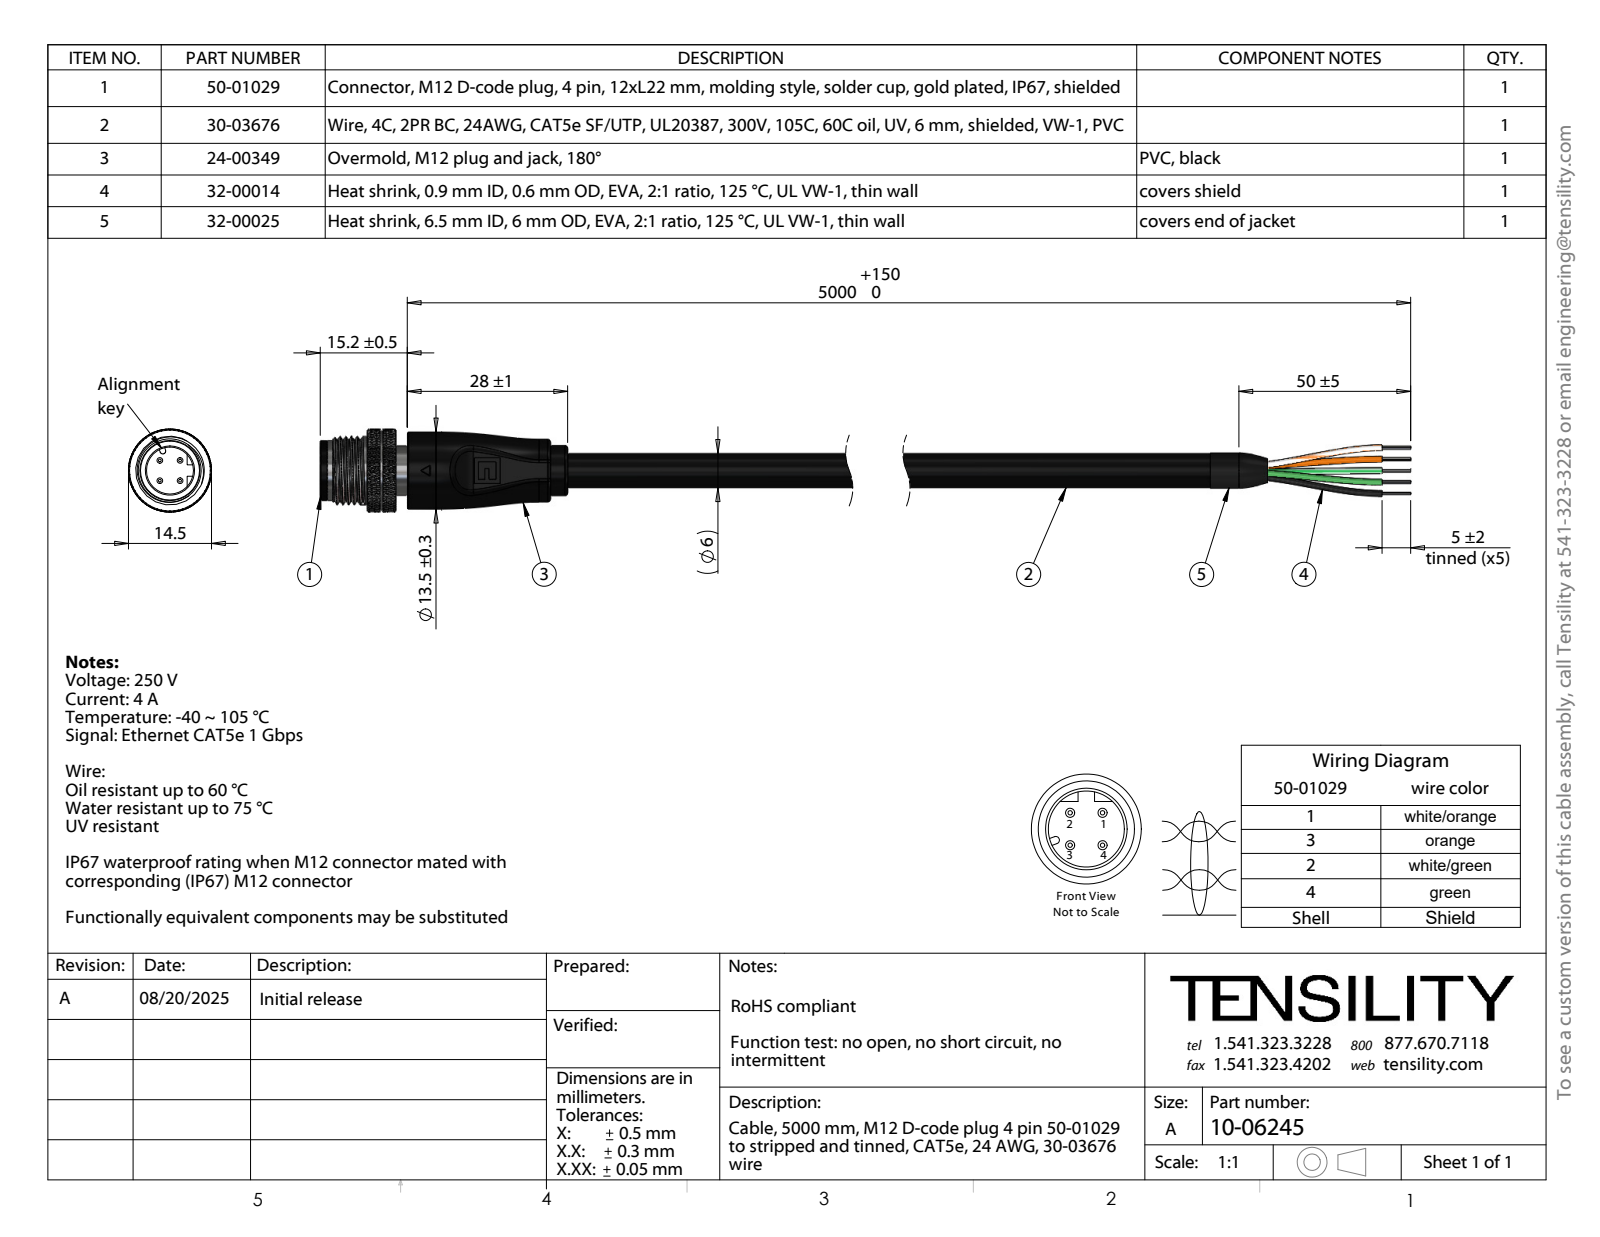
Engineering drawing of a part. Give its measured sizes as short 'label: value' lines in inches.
name: 30-03676_s + t; 24-00349_Mexico; 50-01029-01_默认; 50-01029_默认 (+4 more)
written by: SolidWorks 2025 (CONFIG_CONTROL_DESIGN)
unit: in
bodies: 86 solids, 2792 faces (263 planar, 823 cylindrical, 1706 other)
size: 8.787 × 0.571 × 0.571
volume: 0.567 in³; area: 41 in²
holes: 28× ⌀0.008, 4× ⌀0.039, 4× ⌀0.041, 1× ⌀0.124, 1× ⌀0.126, 1× ⌀0.132, 1× ⌀0.315, 1× ⌀0.323, 1× ⌀0.346, 1× ⌀0.374
bosses: 35× ⌀0.008, 4× ⌀0.055, 1× ⌀0.571, 1× ⌀0.547, 1× ⌀0.531, 1× ⌀0.472, 1× ⌀0.433, 1× ⌀0.413
rounds: 2× R0.02, 2× R0.059, 2× R0.077, 1× R0.197, 1× R0.22, 1× R0.266
face distances: 7.087, 0.276, 0.079, 7.008, 0.197, 1.102, 1.181, 5.906, 0.425, 0.15
hole spacings: 0.075, 0.082, 0.042, 0.014, 0.035, 0.043, 0.049, 0.067
